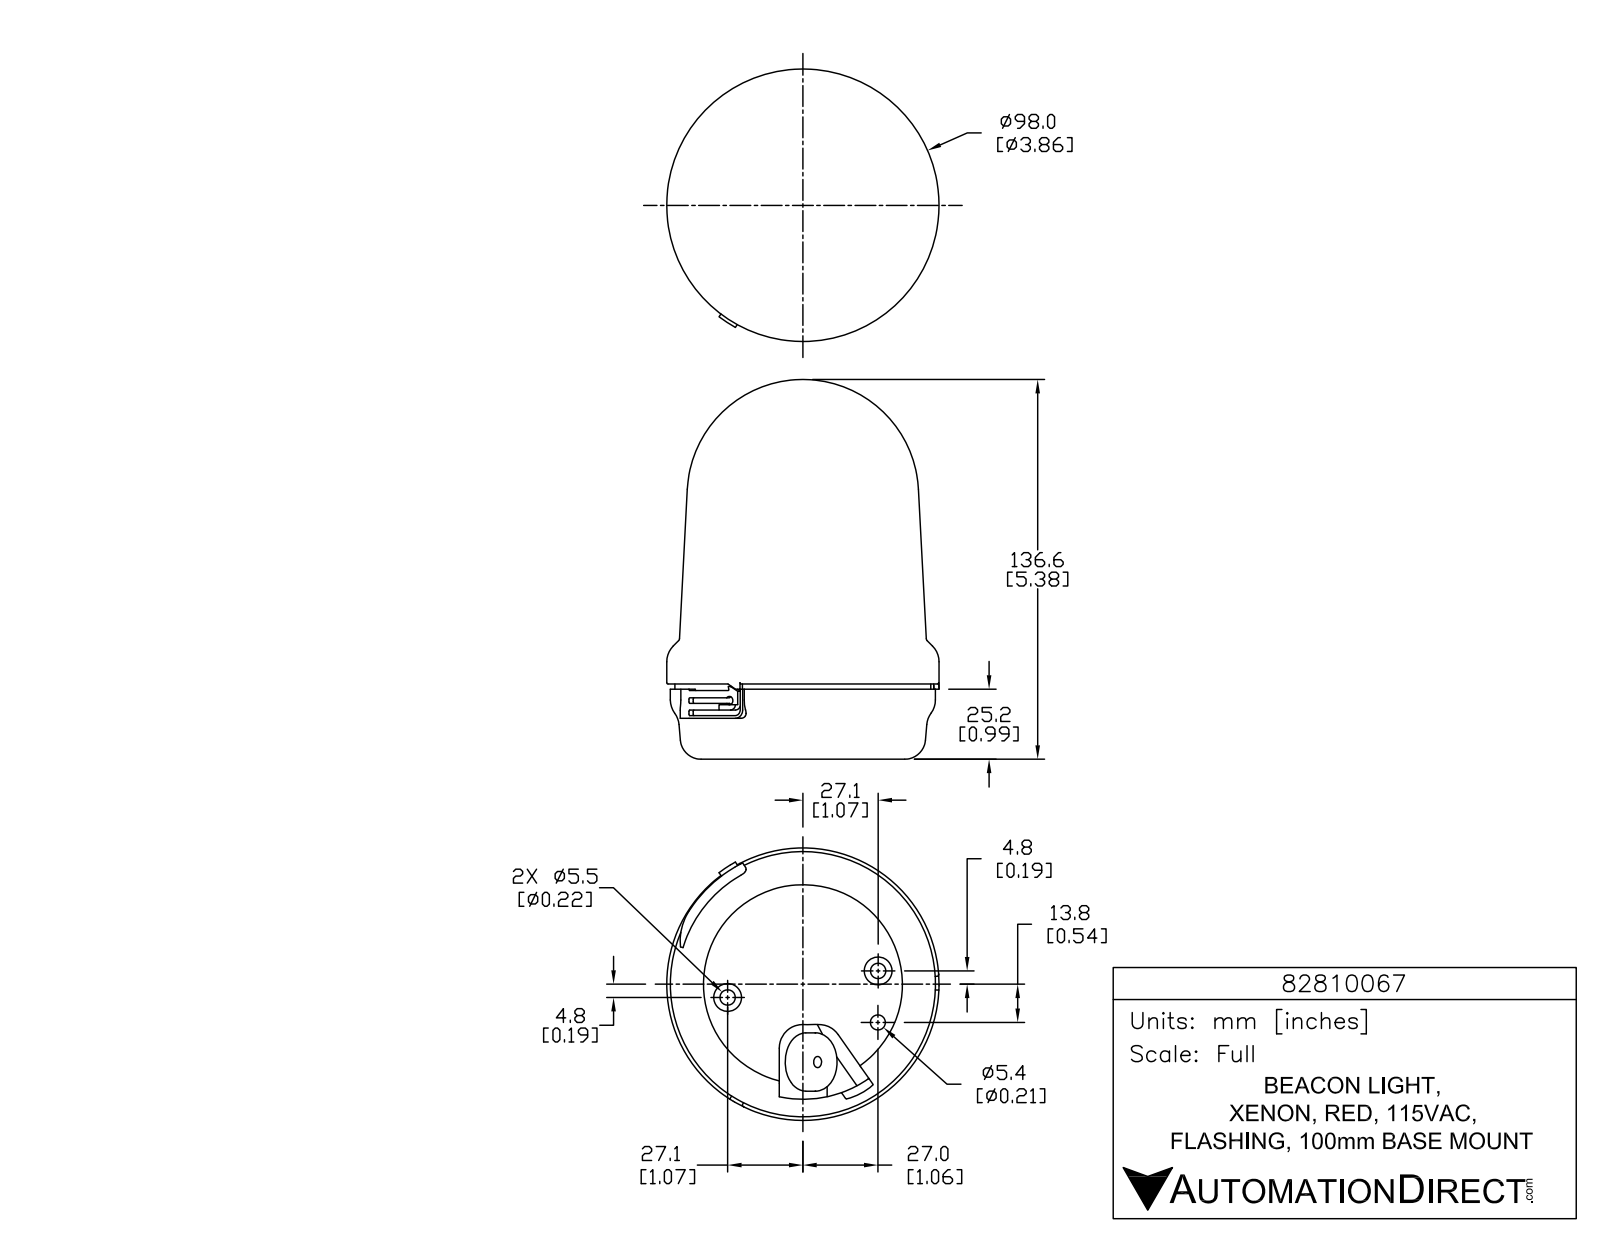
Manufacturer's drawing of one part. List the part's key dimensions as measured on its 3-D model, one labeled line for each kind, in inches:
Part name (STEP PRODUCT): 82810067
STEP written by: SolidWorks 2015 (AUTOMOTIVE_DESIGN)
Units: inches
Bodies: 1 solid, 872 faces (566 planar, 204 cylindrical, 102 other)
Overall size (bounding box): 5.378 × 3.858 × 3.858
Volume: 44.69 in³ · Surface area: 73.66 in²
Round holes (diameter × count): ⌀0.059 ×3, ⌀0.217 ×2, ⌀0.157 ×1, ⌀0.213 ×1, ⌀2.819 ×1
Round bosses / shafts (diameter × count): ⌀0.339 ×3, ⌀0.084 ×3, ⌀0.394 ×2, ⌀3.858 ×1, ⌀3.756 ×1, ⌀3.626 ×1, ⌀0.827 ×1
Partial cylindrical surfaces — rounded edges, fillets, slot ends (radius × count): R0.005 ×9, R0.005 ×6, R0.012 ×6, R0.012 ×6, R0.012 ×6, R0.196 ×6, R0.02 ×5, R0.039 ×4
Main face-to-face distances: 1.045, 0.972, 0.073, 0.02, 0.992, 1.065, 0.236, 0.579, 0.559, 0.413
Hole centre spacings: 1.083, 0.73, 1.193, 2.158, 2.165
